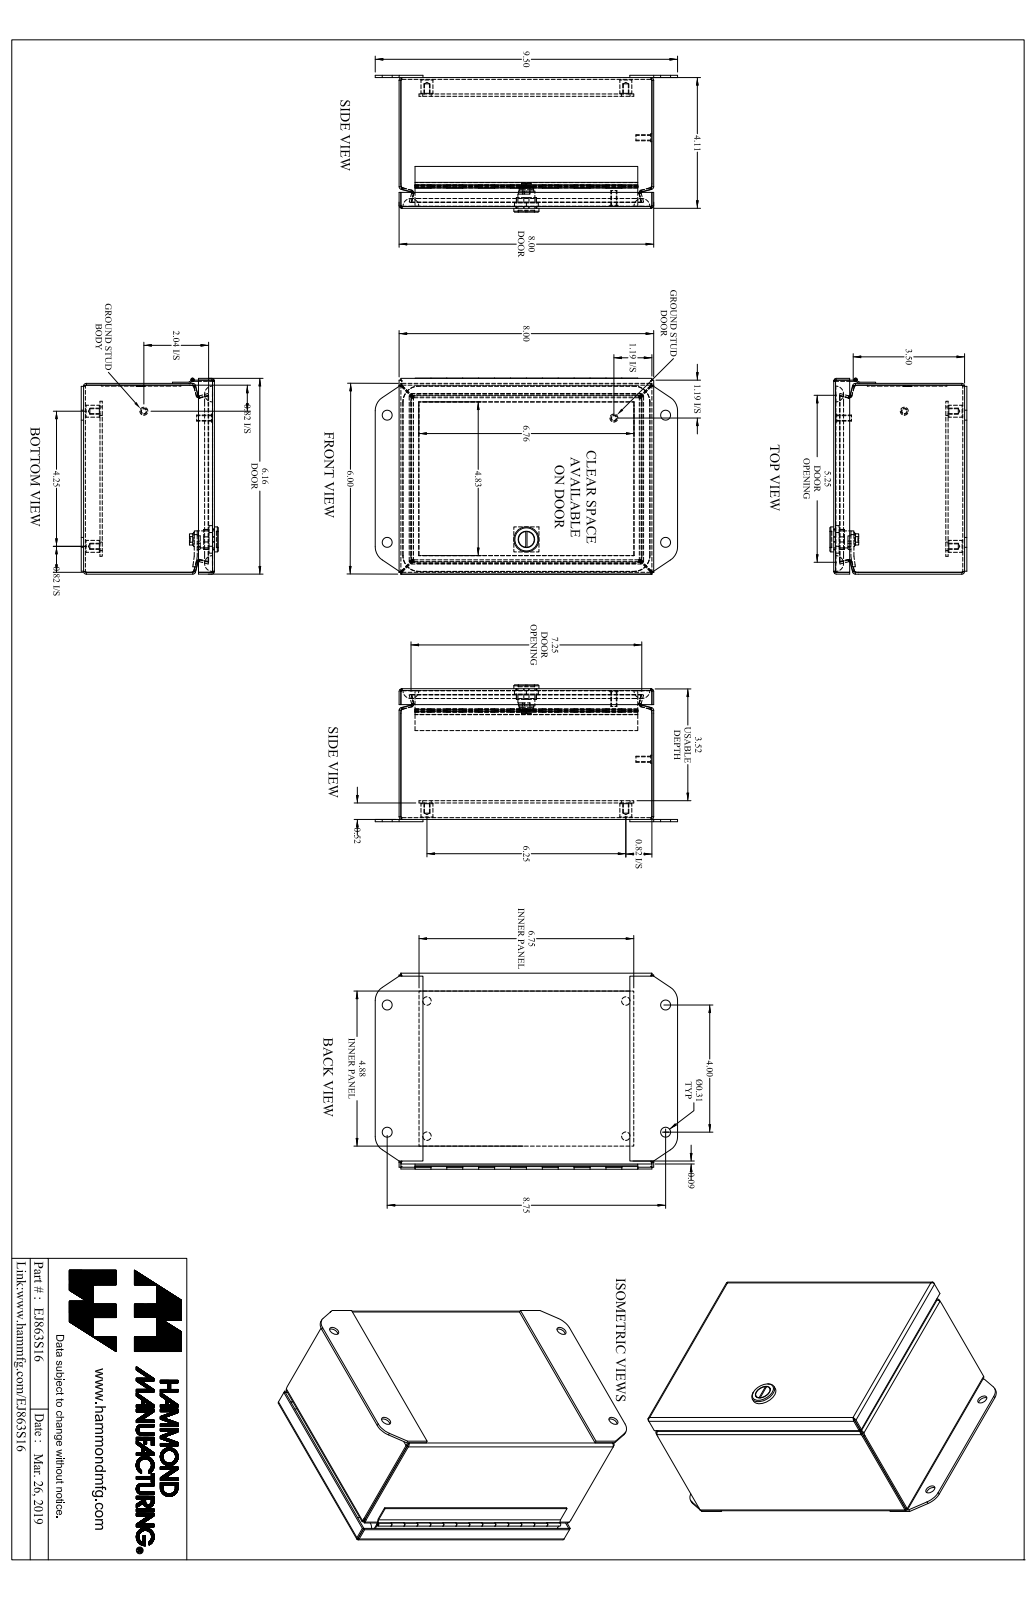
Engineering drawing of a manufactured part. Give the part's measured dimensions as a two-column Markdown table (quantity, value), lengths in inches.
| quantity | value |
| --- | --- |
| part name | EJ863S16_Default |
| STEP written by | SolidWorks 2019 (CONFIG_CONTROL_DESIGN) |
| units | inches |
| bodies | 16 solids, 564 faces (294 planar, 190 cylindrical, 80 other) |
| overall size | 9.5 × 6.165 × 4.305 |
| volume | 19.35 in³ |
| surface area | 636 in² |
| round holes (diameter × count) | 0.156 × 4, 0.265 × 4, 0.313 × 4, 0.05 × 1, 0.516 × 1 |
| round bosses / shafts (diameter × count) | 0.375 × 4, 0.25 × 2, 0.19 × 2, 0.788 × 1, 0.535 × 1, 0.496 × 1, 0.435 × 1, 0.1 × 1 |
| partial cylindrical surfaces (radius × count) | 0.029 × 16, 0.086 × 16, 0.281 × 12, 0.25 × 4, 0.499 × 4, 0.5 × 4, 0.06 × 2, 0.03 × 1 |
| main face-to-face distances | 0.057, 4.054, 5.943, 0.072, 0.589, 4.111, 3.997, 7.943, 3.594, 3.537 |
| hole center spacings | 1.256, 4.31, 7.502, 8.56, 3.133, 4, 4.25, 4.376 |
